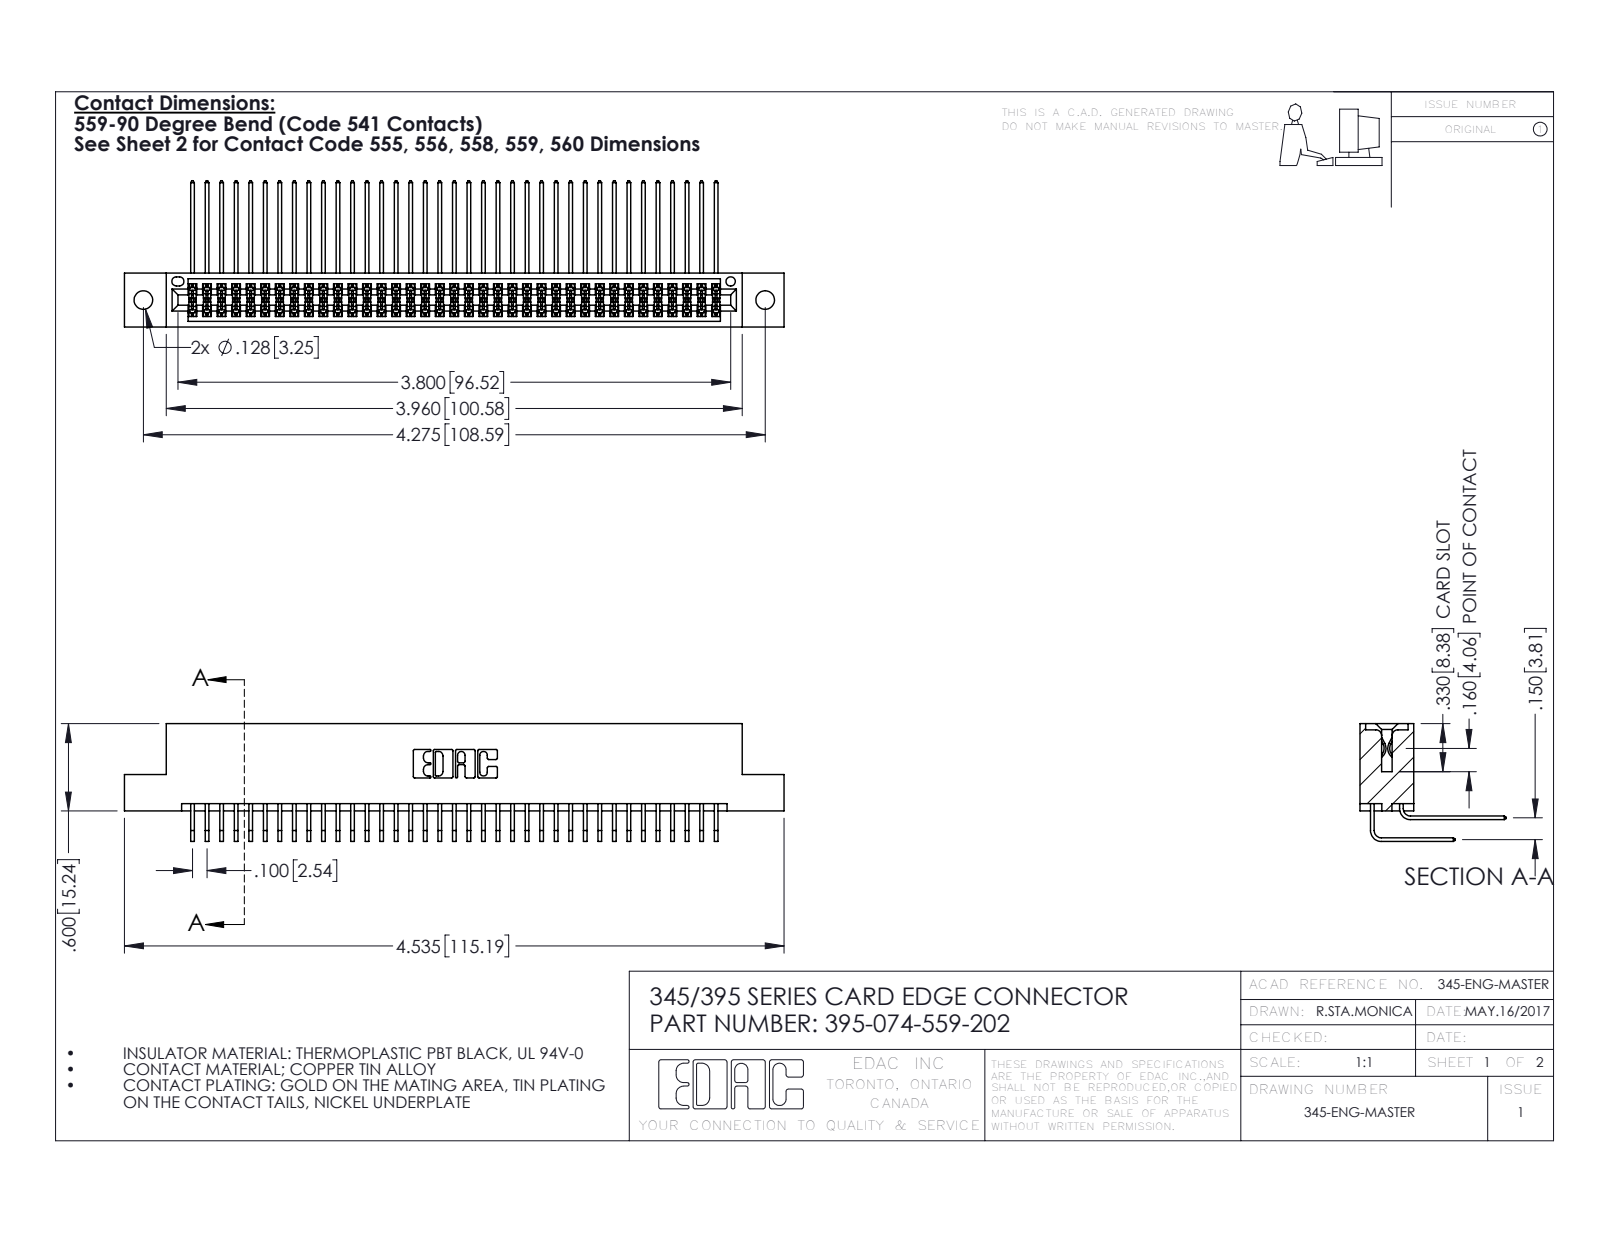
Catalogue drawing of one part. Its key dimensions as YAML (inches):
part_name: "345 Part_Flush Mounting Lugs - 0.128 Dia; 395-074-559-202; 345-292-001_558 559 Tail - 1; 345-292-001_559 Tail - 2"
step_written_by: "SolidWorks 2016 (CONFIG_CONTROL_DESIGN)"
units: inches
bodies: {solids: 75, faces: 3974, planar: 2670, cylindrical: 1304, other: 0}
overall_size: [4.535, 1.005, 0.809]
volume: 0.704
surface_area: 28.96
round_holes:
  - {diameter: 0.128, count: 2}
  - {diameter: 0.064, count: 1}
partial_cylinders:
  - {radius: 0.006, count: 112}
  - {radius: 0.01, count: 22}
  - {radius: 0.007, count: 6}
  - {radius: 0.031, count: 6}
  - {radius: 0.026, count: 3}
  - {radius: 0.014, count: 2}
  - {radius: 0.019, count: 2}
  - {radius: 0.022, count: 2}
face_to_face_distances: [0.072, 0.298, 0.2, 0.37, 0.098, 0.272, 0.025, 0.225, 0.175, 0.15]
hole_center_spacings: [0.27, 4.039, 4.275]
